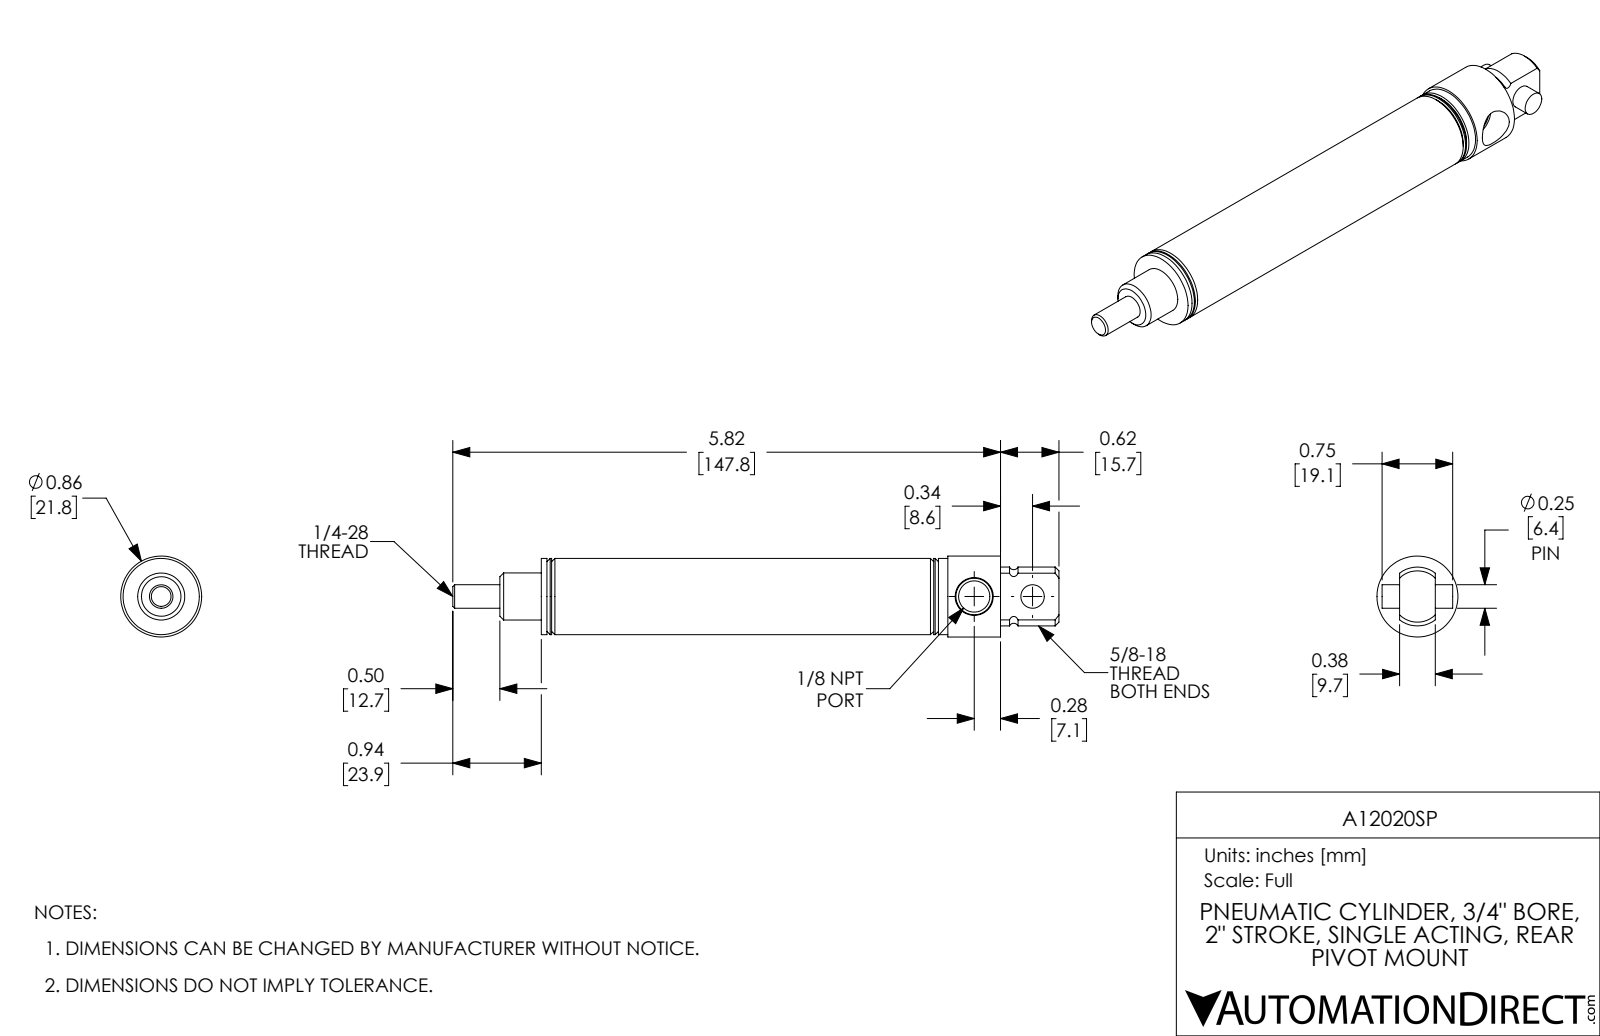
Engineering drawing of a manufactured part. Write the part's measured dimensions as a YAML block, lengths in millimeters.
part_name: "A12020SP-MainBody; A12020SP-Rod; A12020SP-Pin; A12020SP"
step_written_by: "SolidWorks 2017 (AUTOMOTIVE_DESIGN)"
units: millimeters
bodies: {solids: 3, faces: 73, planar: 19, cylindrical: 32, other: 22}
overall_size: [163.6, 21.8, 21.8]
volume: 32320
surface_area: 19700
round_holes:
  - {diameter: 6.4, count: 2}
  - {diameter: 8.4, count: 1}
  - {diameter: 19.1, count: 1}
round_bosses_or_shafts:
  - {diameter: 21.8, count: 1}
  - {diameter: 20.6, count: 1}
  - {diameter: 12.7, count: 1}
partial_cylinders:
  - {radius: 8, count: 1}
face_to_face_distances: [12.7, 63.5, 50.8, 30.2, 42.9, 93.7, 124, 93.7, 81, 30.2]
hole_center_spacings: [15.7]
